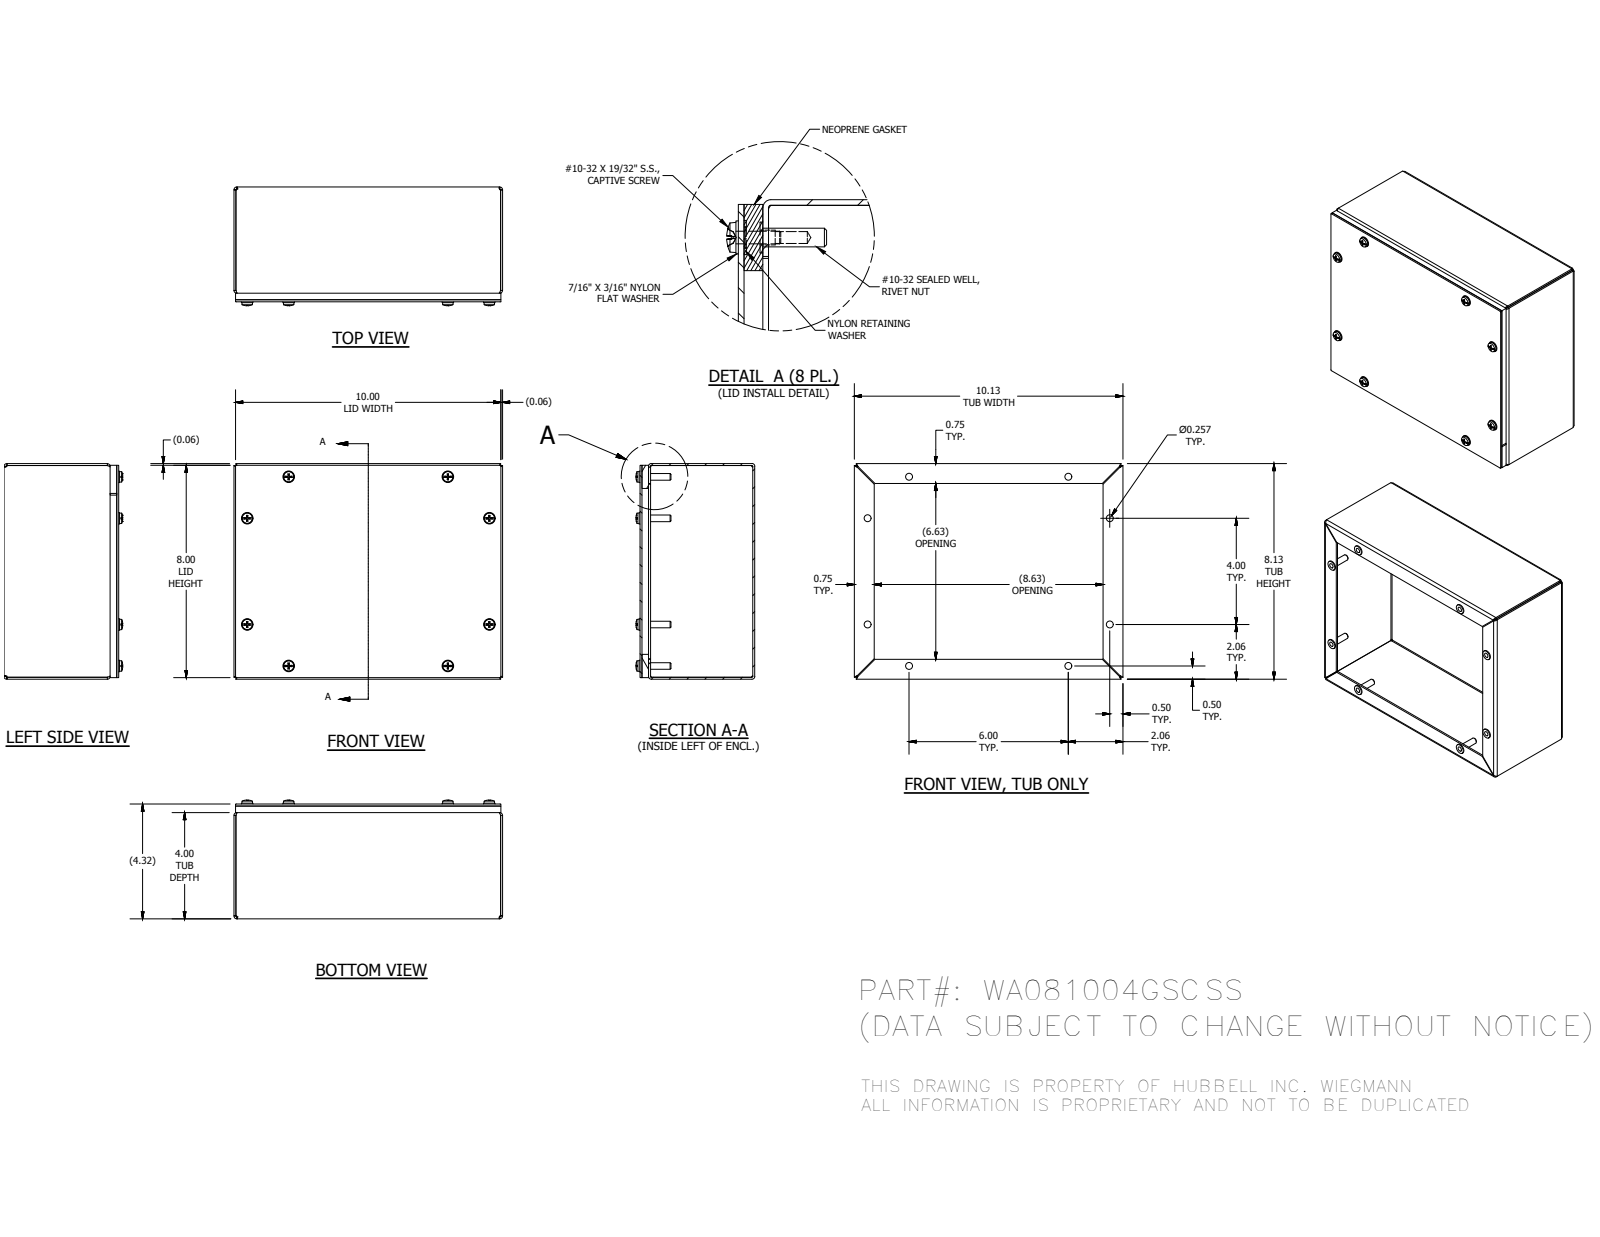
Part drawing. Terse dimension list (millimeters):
name: WA081004GSCSSBKP; WA0810GSCSSLID; 316296; 37210 (+4 more)
written by: Autodesk Inventor 2016 (AUTOMOTIVE_DESIGN)
unit: mm
bodies: 36 solids, 764 faces (420 planar, 160 cylindrical, 184 other)
size: 257.18 × 206.38 × 113.75
volume: 513 575 mm³; area: 483 952 mm²
holes: 8× ⌀3.96, 8× ⌀4.78, 8× ⌀4.98, 8× ⌀6.53, 8× ⌀7.06, 8× ⌀7.14, 8× ⌀7.95
bosses: 8× ⌀11.51, 8× ⌀11.11, 8× ⌀10.31, 8× ⌀6.3, 8× ⌀4.25
rounds: 12× R0.79, 8× R1.78, 8× R2.27, 8× R2.67
face distances: 1.88, 107.95, 109.83, 106.07, 204.5, 99.72, 8.23, 255.3, 6.35, 101.6
hole spacings: 56.12, 101.6, 152.4, 238.44, 56.1, 56.13, 146.73, 146.74
